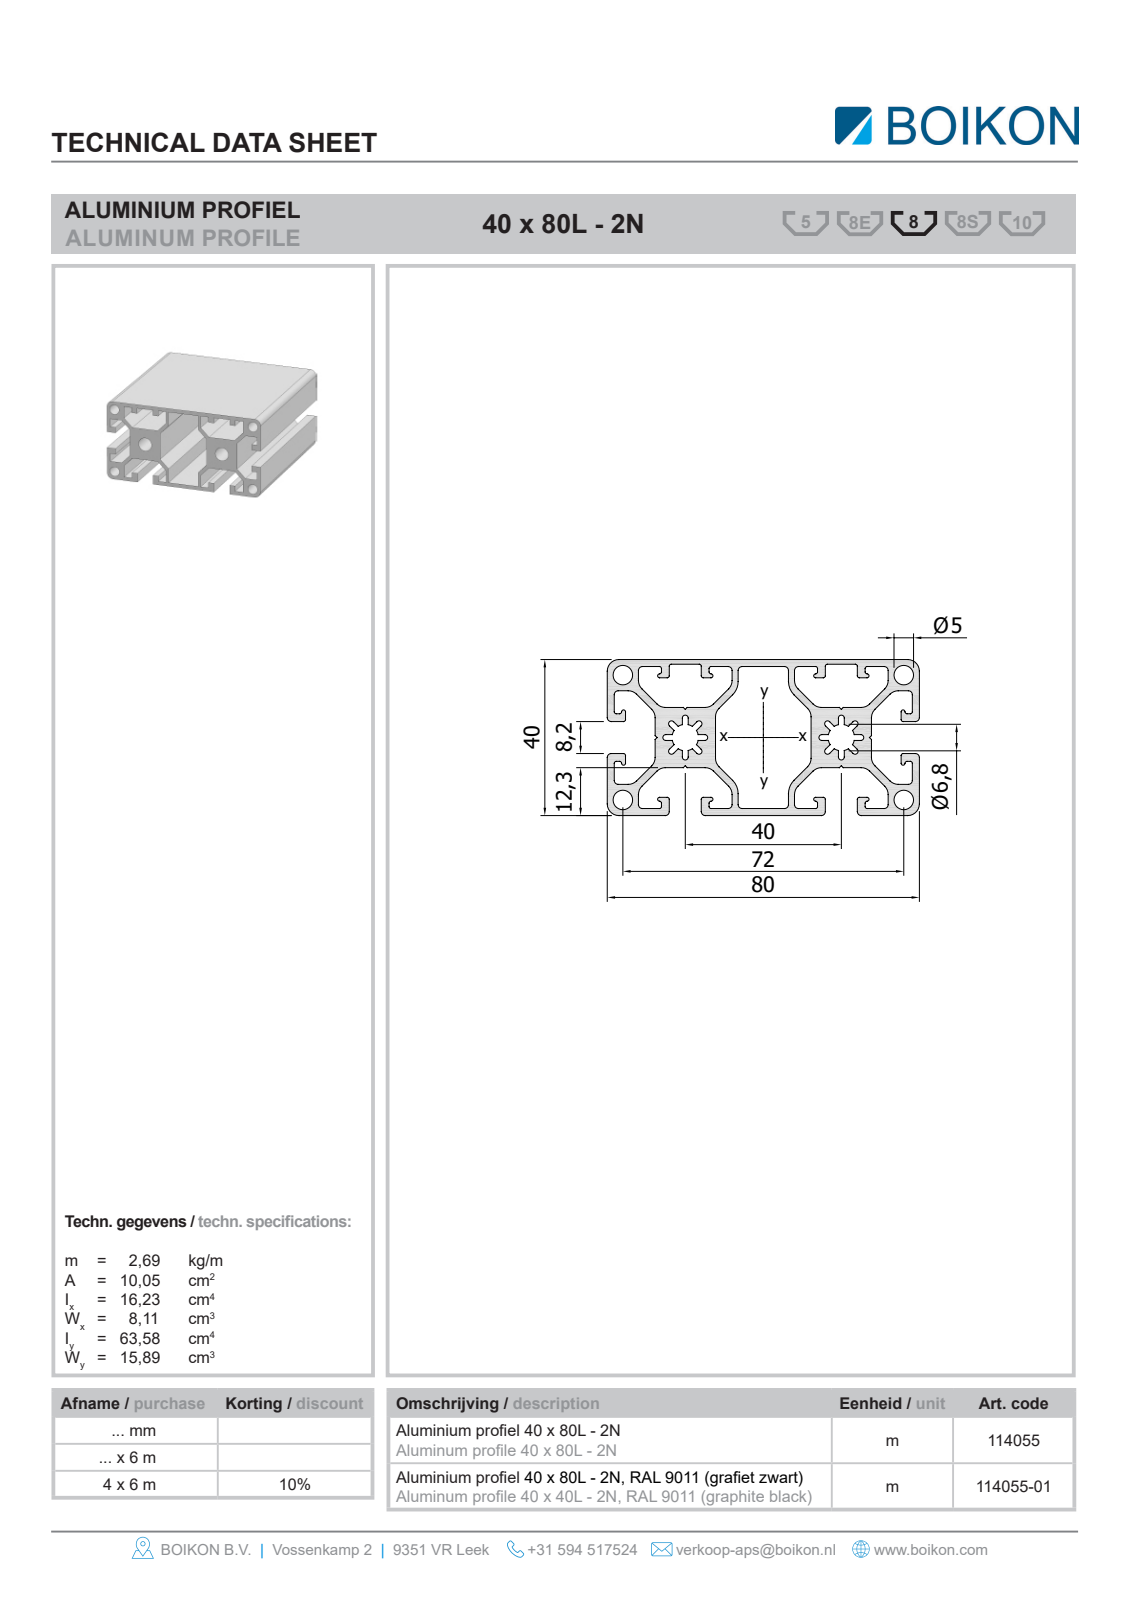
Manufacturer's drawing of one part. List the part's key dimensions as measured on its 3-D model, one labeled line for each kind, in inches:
Part name (STEP PRODUCT): Root; 11405540x80L-2NBOIKON0
STEP written by: HiCAD 2013 1802.4 Build 509 (AUTOMOTIVE_DESIGN)
Units: inches
Bodies: 1 solid, 112 faces (102 planar, 10 cylindrical, 0 other)
Overall size (bounding box): 39.37 × 3.15 × 1.575
Volume: 67.8 in³ · Surface area: 1 277 in²
Round holes (diameter × count): ⌀0.197 ×4, ⌀0.268 ×2
Partial cylindrical surfaces — rounded edges, fillets, slot ends (radius × count): R0.118 ×4
Main face-to-face distances: 0.071, 1.575, 1.504, 0.476, 1.098, 0.122, 0.744, 0.406, 1.028, 0.177
Hole centre spacings: 0.891, 2.293, 1.26, 2.835, 3.102, 1.575
